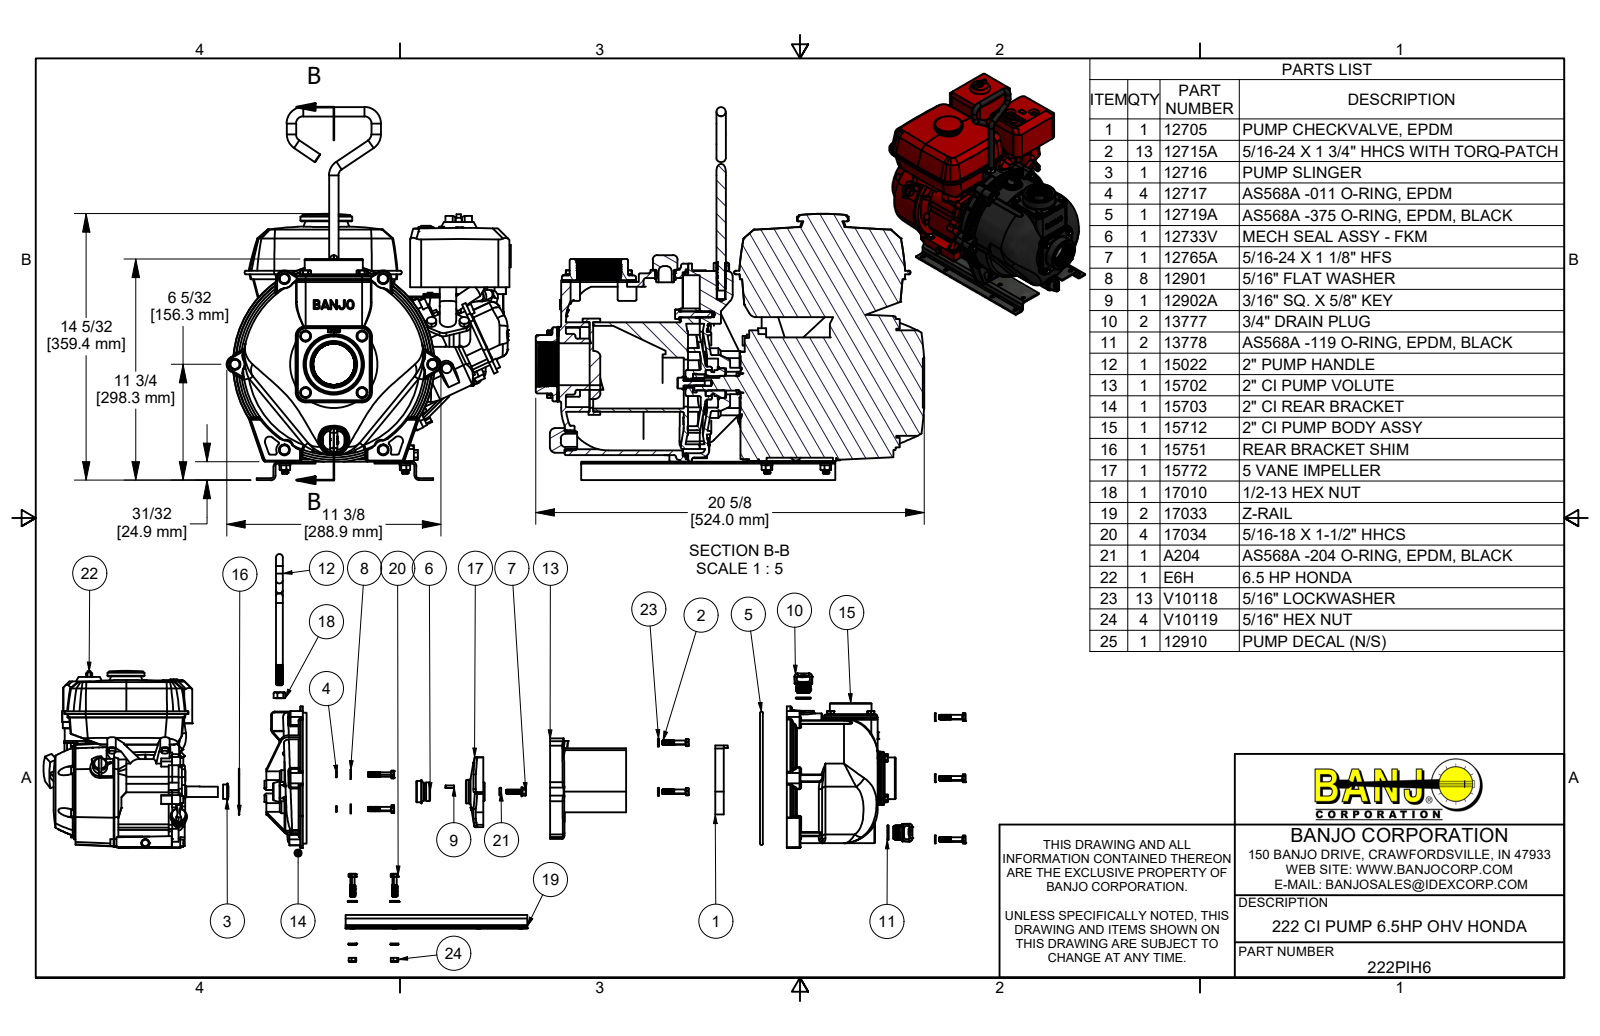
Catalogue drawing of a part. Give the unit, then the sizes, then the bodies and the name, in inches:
Units: inches
Overall size (bounding box): 46.336 × 38.272 × 15.096
Round holes (diameter × count): ⌀0.322 ×21, ⌀0.344 ×18, ⌀0.267 ×10, ⌀0.252 ×8, ⌀0.359 ×8, ⌀0.375 ×8, ⌀0.323 ×7, ⌀0.252 ×4, ⌀0.425 ×4, ⌀0.815 ×4, ⌀0.25 ×2, ⌀0.7 ×2
Round bosses / shafts (diameter × count): ⌀0.276 ×260, ⌀0.268 ×164, ⌀0.313 ×25, ⌀0.583 ×21, ⌀1 ×8, ⌀0.688 ×8, ⌀0.512 ×6, ⌀0.5 ×5
Partial cylindrical surfaces — rounded edges, fillets, slot ends (radius × count): R0.125 ×120, R0.06 ×97, R0.138 ×26, R0.079 ×24, R0.25 ×22, R0.5 ×21, R0.469 ×18, R0.284 ×17
Main face-to-face distances: 0.105, 0.25, 0.18, 0.094, 0.875, 2.88, 7.778, 7.673, 0.217, 9.367
Hole centre spacings: 5.25, 1.063, 3, 7.441, 8.07, 5.25, 9.093, 3.248
Volume: 1 178 in³ · Surface area: 3 576 in²
Bodies: 89 solids, 9130 faces (2199 planar, 3078 cylindrical, 3853 other)
Part name (STEP PRODUCT): 222PIH6; 15703; 15712; 15712X (+8 more)
STEP written by: Autodesk Inventor 2019 (AUTOMOTIVE_DESIGN)
